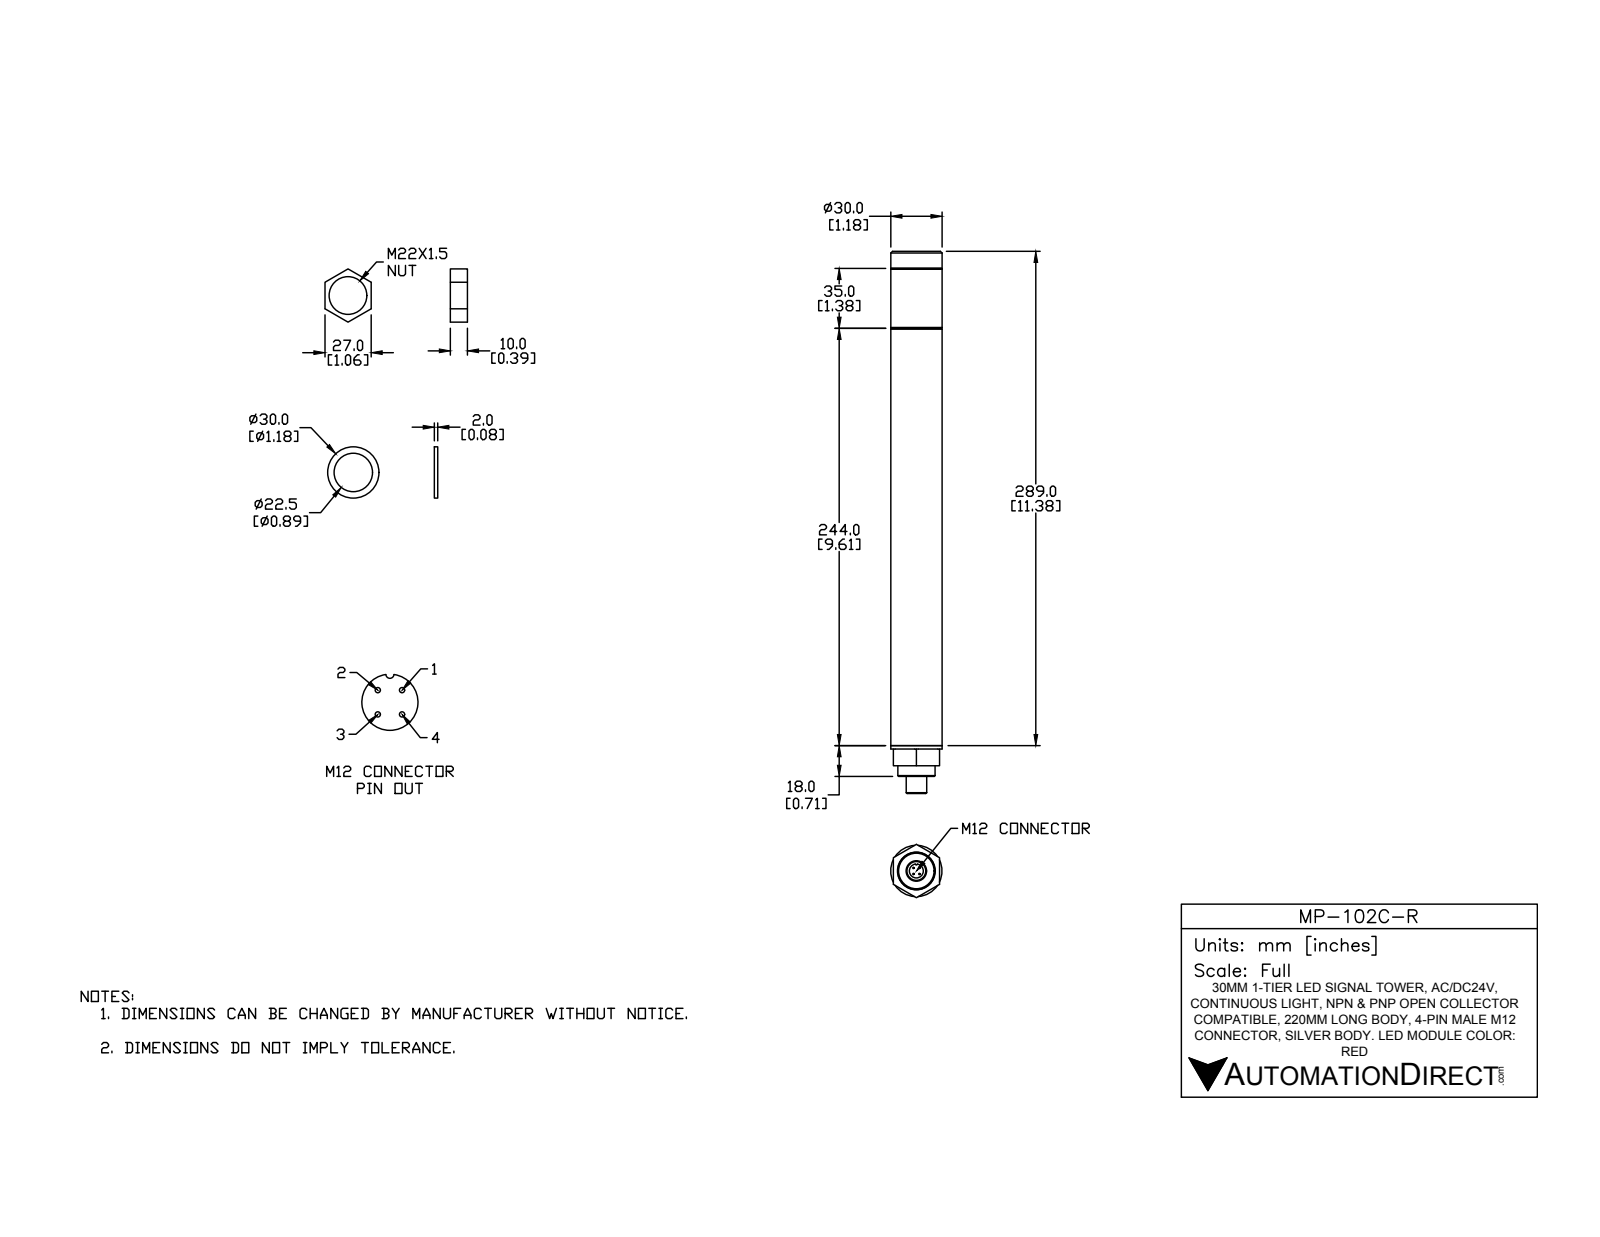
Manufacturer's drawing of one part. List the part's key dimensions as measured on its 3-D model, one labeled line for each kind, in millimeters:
Part name (STEP PRODUCT): MP-102C-R
STEP written by: SolidWorks 2016 (AUTOMOTIVE_DESIGN)
Units: millimetres
Bodies: 10 solids, 98 faces (41 planar, 35 cylindrical, 22 other)
Overall size (bounding box): 317 × 31.18 × 30
Volume: 203 438 mm³ · Surface area: 39 323 mm²
Round holes (diameter × count): ⌀3.2 ×1, ⌀7.7 ×1, ⌀8.2 ×1, ⌀20.7 ×1, ⌀22 ×1
Round bosses / shafts (diameter × count): ⌀0.75 ×4, ⌀30 ×1, ⌀21.8 ×1, ⌀12 ×1, ⌀5 ×1
Partial cylindrical surfaces — rounded edges, fillets, slot ends (radius × count): R0.6 ×1
Main face-to-face distances: 35, 244, 279, 246, 10, 2, 281, 289, 291, 45
